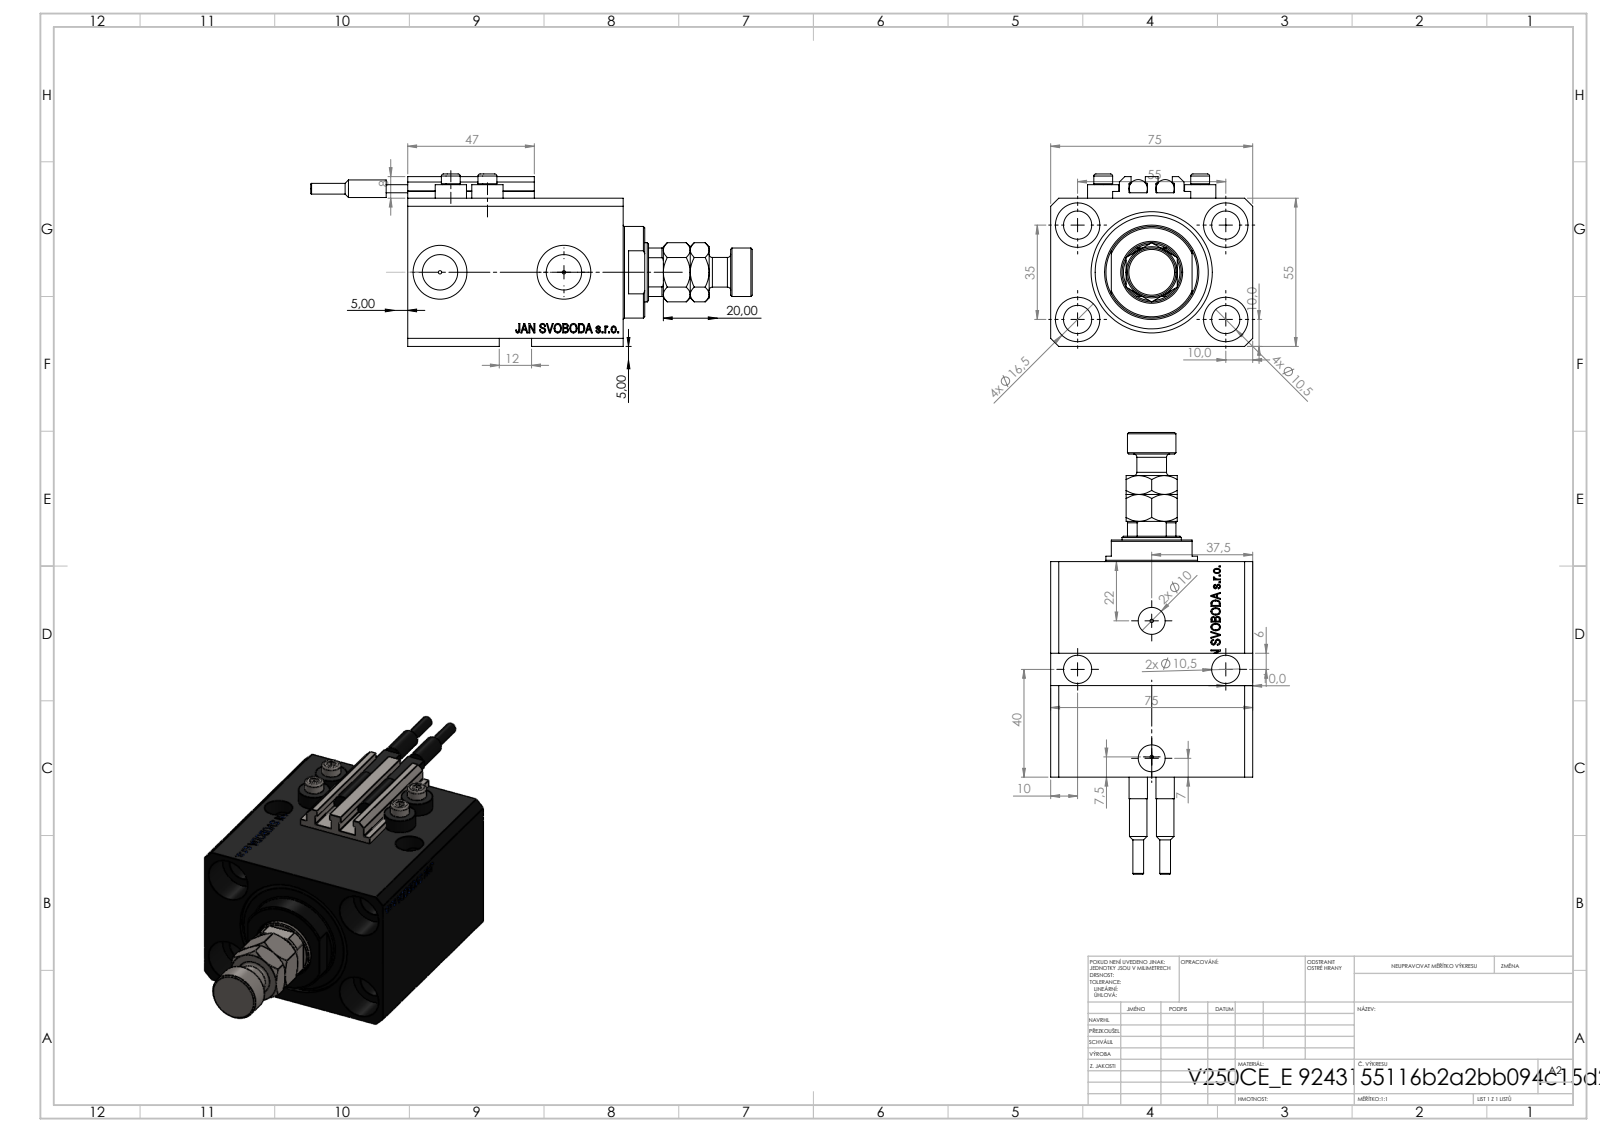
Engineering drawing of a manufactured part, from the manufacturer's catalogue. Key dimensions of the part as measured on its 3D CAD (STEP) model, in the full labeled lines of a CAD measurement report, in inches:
Part name (STEP PRODUCT): MFA; V250CE_VC_E; ALLEN BOLT V250CE; V250CE_E_Body (+2 more)
STEP written by: SolidWorks 2019 (CONFIG_CONTROL_DESIGN)
Units: inches
Bodies: 11 solids, 1168 faces (562 planar, 142 cylindrical, 464 other)
Overall size (bounding box): 6.457 × 2.953 × 2.52
Volume: 18.03 in³ · Surface area: 123.9 in²
Round holes (diameter × count): ⌀0.413 ×7, ⌀0.049 ×4, ⌀0.157 ×4, ⌀0.65 ×4, ⌀0.394 ×2, ⌀0.518 ×2, ⌀0.787 ×2, ⌀0.866 ×1, ⌀1.26 ×1, ⌀1.772 ×1
Round bosses / shafts (diameter × count): ⌀0.457 ×4, ⌀0.276 ×4, ⌀0.268 ×2, ⌀0.256 ×2, ⌀0.157 ×2, ⌀1.339 ×1, ⌀0.709 ×1, ⌀0.433 ×1
Partial cylindrical surfaces — rounded edges, fillets, slot ends (radius × count): R0.008 ×10, R0.413 ×1
Main face-to-face distances: 2.165, 2.953, 0.591, 3.15, 0.118, 2.559, 2.169, 0.39, 2.244, 2.76
Hole centre spacings: 1.283, 2.165, 0.535, 0.555, 0.783, 0.792, 1.016, 1.121
